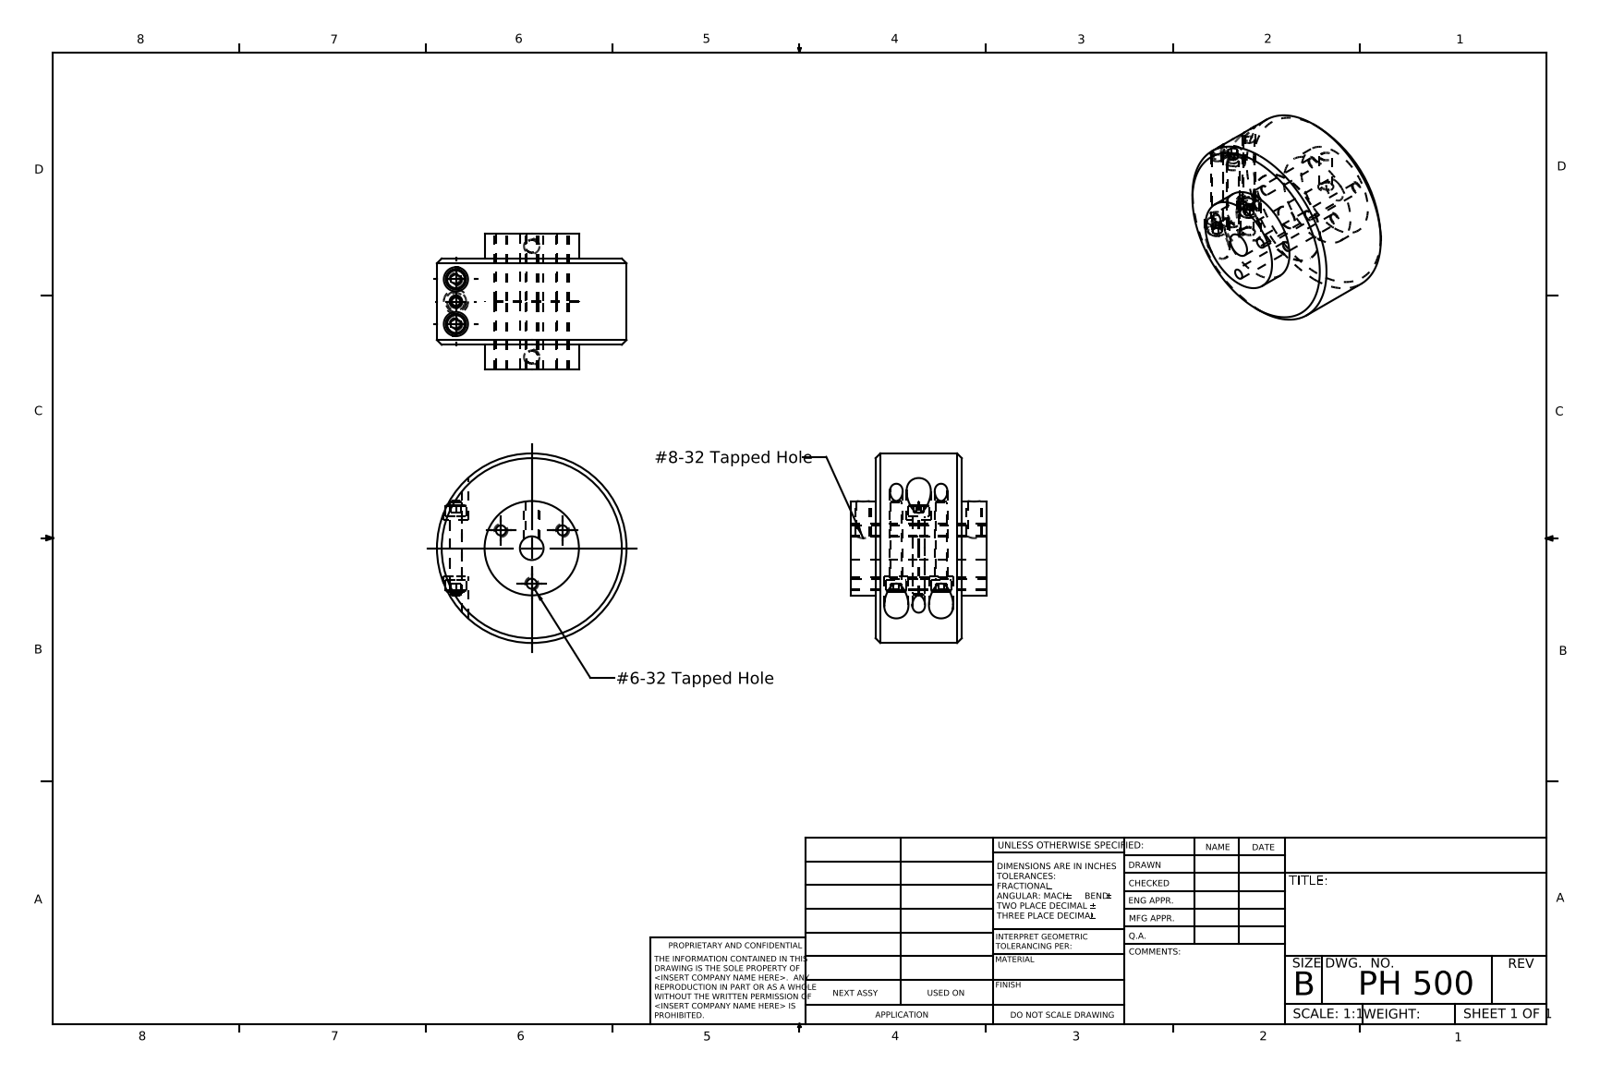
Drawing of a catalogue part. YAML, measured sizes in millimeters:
part_name: "PH 500"
step_written_by: "SolidWorks 2010 (CONFIG_CONTROL_DESIGN)"
units: millimeters
bodies: {solids: 4, faces: 107, planar: 39, cylindrical: 52, other: 16}
overall_size: [50.8, 50.8, 36.3]
volume: 50490
surface_area: 13140
round_holes:
  - {diameter: 2.7, count: 3}
  - {diameter: 3.4, count: 3}
  - {diameter: 6.5, count: 3}
  - {diameter: 3.5, count: 2}
  - {diameter: 6.4, count: 1}
round_bosses_or_shafts:
  - {diameter: 5.5, count: 3}
  - {diameter: 3, count: 3}
  - {diameter: 50.8, count: 1}
  - {diameter: 25.3, count: 1}
face_to_face_distances: [23.1, 11.5, 11.6, 6.6, 18.1, 18.2, 29.7, 36.3, 1, 19.2]
hole_center_spacings: [16.5, 6, 9.5, 22.2, 25.2, 29.1, 9.5, 12]
